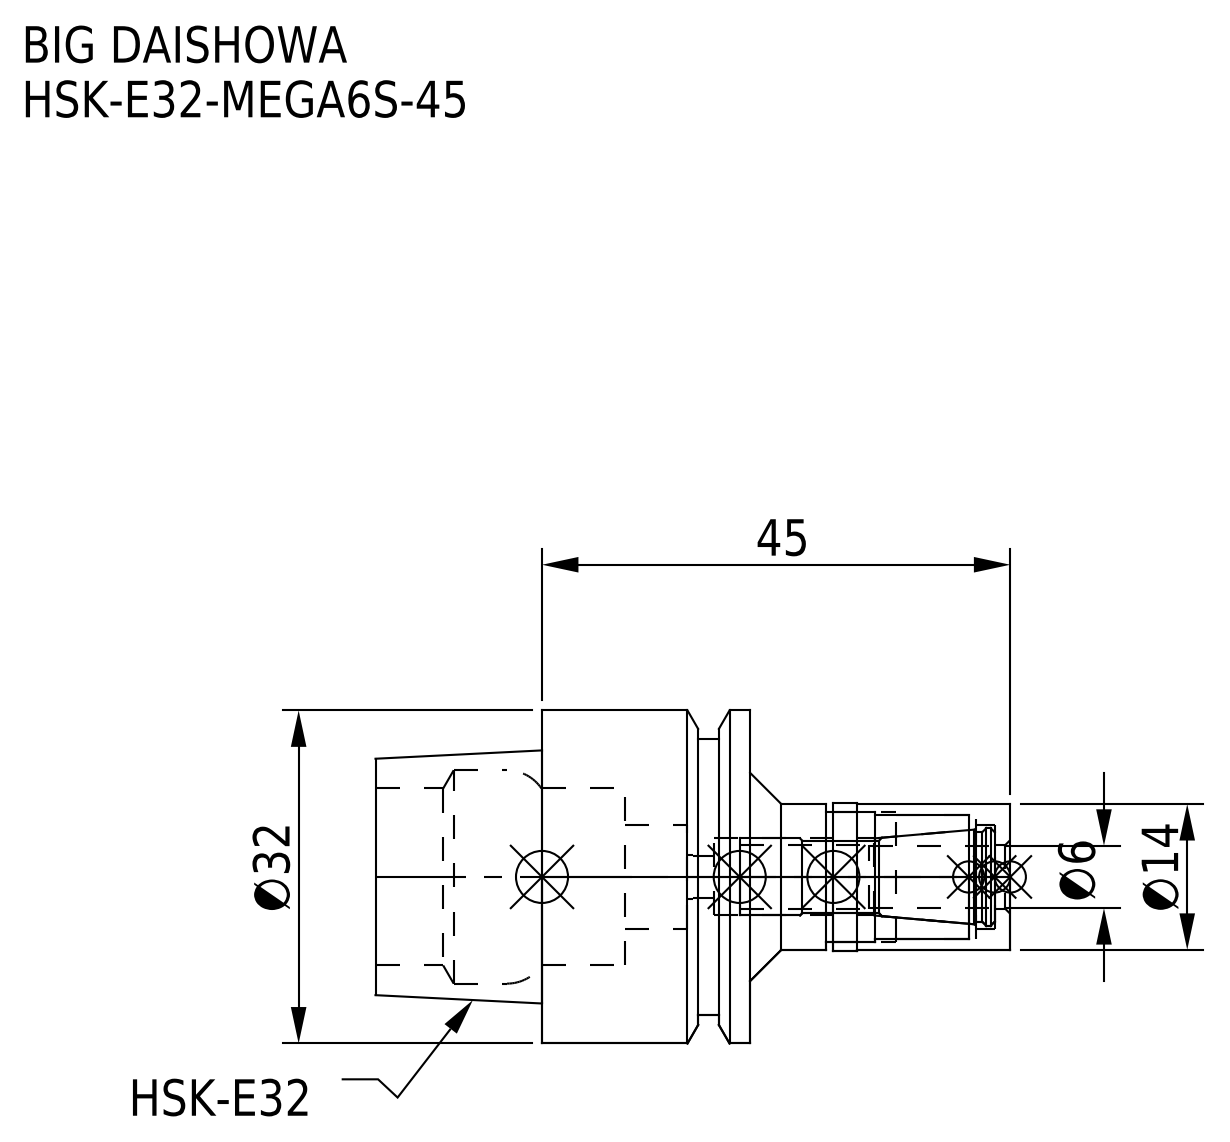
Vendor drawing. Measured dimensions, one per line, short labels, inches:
name: MGN6S_1.stp; HSK-E32-MEGA6S-45; HSK-E32-MEGA6S-45-060-FreeParts; DXF_TEMP_ASSY_ASM_4_ASM.stp (+3 more)
written by: SolidWorks 2019 (CONFIG_CONTROL_DESIGN)
unit: in
bodies: 2 solids, 74 faces (18 planar, 40 cylindrical, 16 other)
size: 2.402 × 1.26 × 1.26
volume: 1.113 in³; area: 15.01 in²
holes: 1× ⌀0.161, 1× ⌀0.165, 1× ⌀0.24, 1× ⌀0.291, 1× ⌀0.394, 1× ⌀0.472, 1× ⌀0.492, 1× ⌀0.669, 1× ⌀0.807
bosses: 1× ⌀1.26, 1× ⌀1.043, 1× ⌀0.563, 1× ⌀0.551
face distances: 0.787, 1.417, 0.63, 0.474, 0.313, 0.943, 0.669, 1.102, 0.984, 1.459
